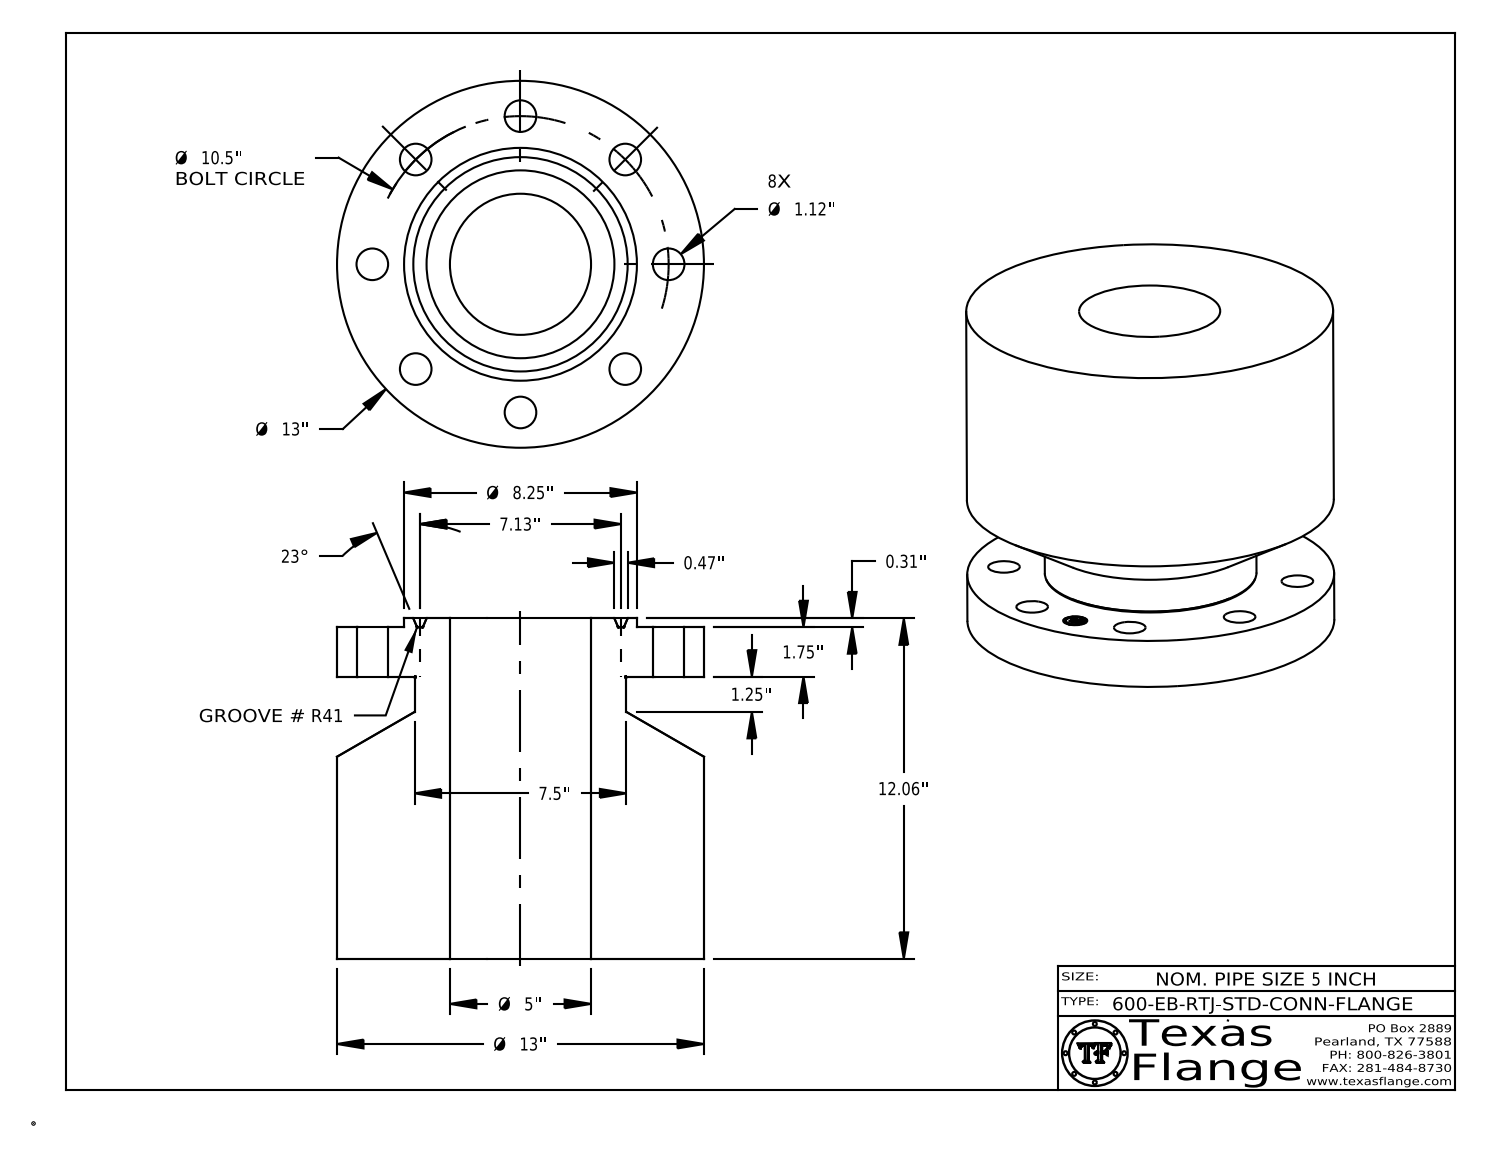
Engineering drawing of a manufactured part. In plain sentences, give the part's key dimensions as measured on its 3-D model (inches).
The part is named "5-600-EB-RTJ-STD-CONN-FLANGE". Its 3-D file was written by "CATIA V5 STEP AP214 (AUTOMOTIVE_DESIGN)". It is 1 solid with 431 faces: 371 planar, 46 cylindrical and 14 other. Overall it measures 13 by 13 by 12.063 inches. Its volume is 1 136 cubic inches and its surface area 1 052 square inches. Round holes: 8 of diameter 1.12, 1 of diameter 0.85, 1 of diameter 5. Round bosses or shafts: 8 of diameter 0.051, 1 of diameter 13, 1 of diameter 8.25, 1 of diameter 7.5, 1 of diameter 0.67. The main face-to-face distances are 10, 1.75, 11.75, 0.313, 2.063, 12.063, 2.058, 1.745, 10.005, 0.254. The hole center spacings are 5.25, 4.018, 9.701, 7.424, 7.425, 2.048, 5.833, 8.73.
